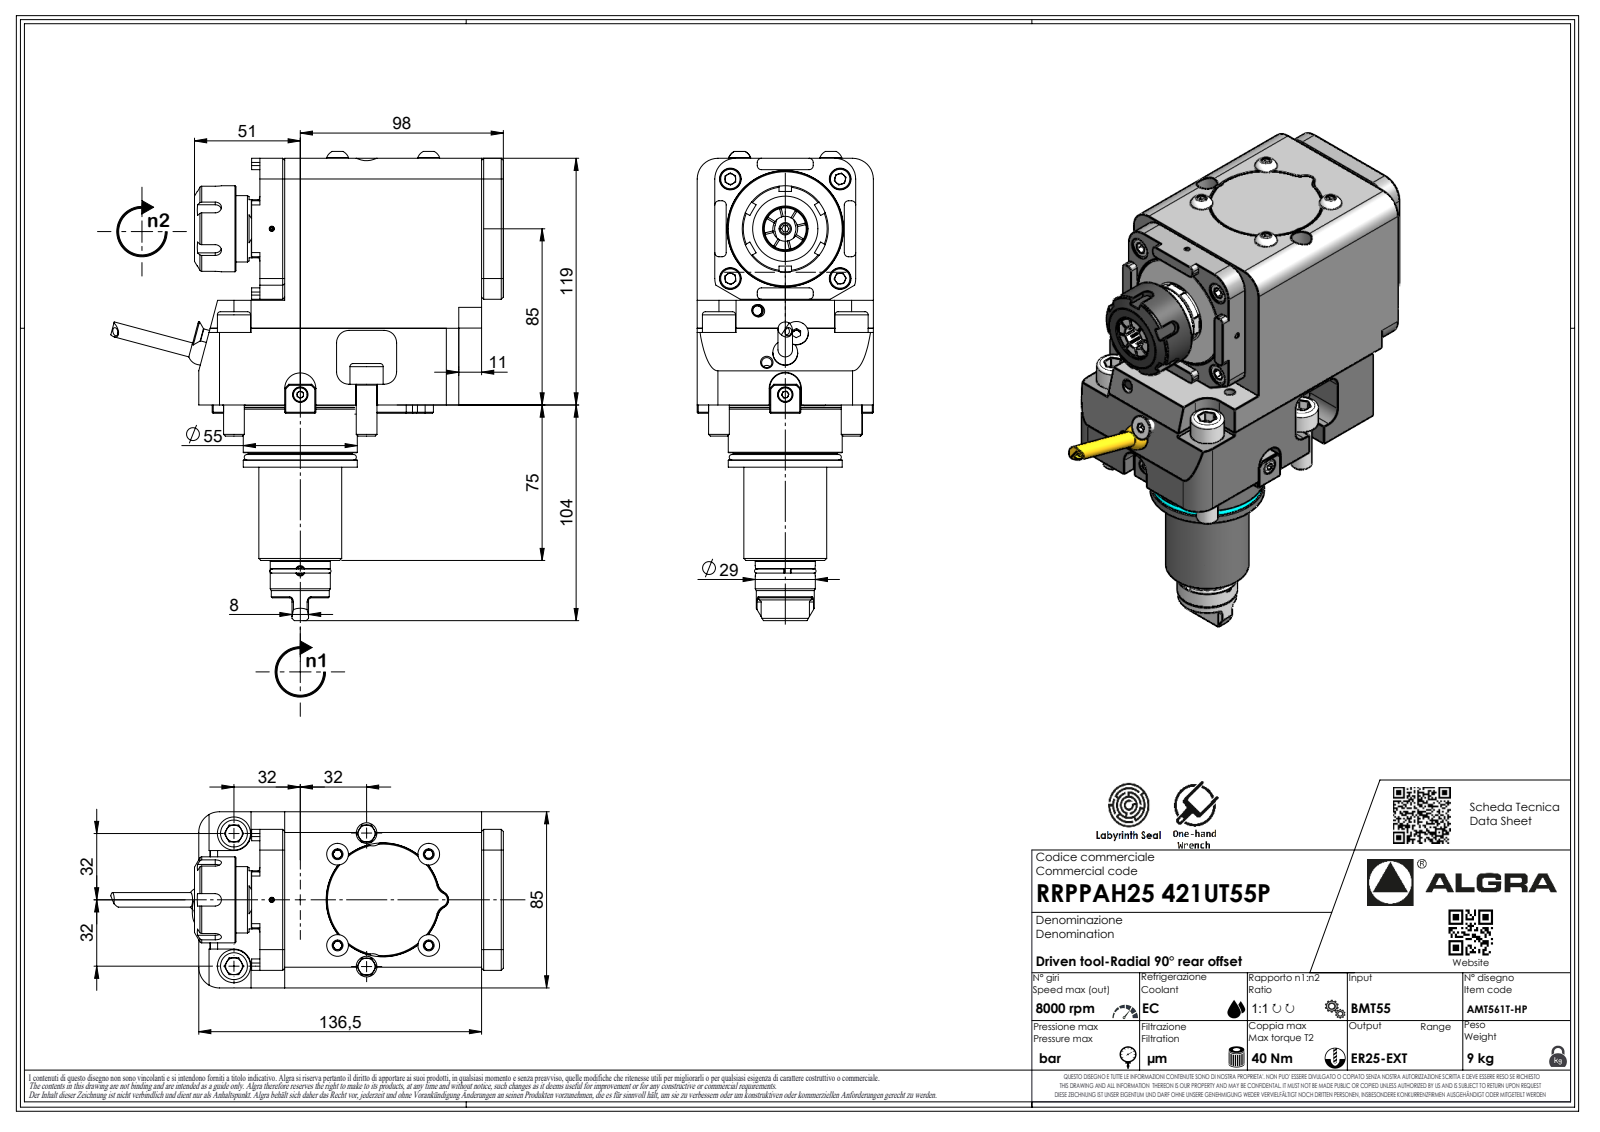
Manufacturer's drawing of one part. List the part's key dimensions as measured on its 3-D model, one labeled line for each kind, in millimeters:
Part name (STEP PRODUCT): RRPPAH25421UT55P
STEP written by: SolidWorks 2023 (AUTOMOTIVE_DESIGN)
Units: millimetres
Bodies: 6 solids, 925 faces (580 planar, 163 cylindrical, 182 other)
Overall size (bounding box): 226.3 × 189.45 × 85
Volume: 1 300 000 mm³ · Surface area: 127 205 mm²
Round holes (diameter × count): ⌀10.5 ×2, ⌀12 ×2, ⌀2.1 ×1, ⌀4 ×1, ⌀5 ×1, ⌀6 ×1, ⌀8.8 ×1, ⌀60 ×1
Round bosses / shafts (diameter × count): ⌀16 ×4, ⌀10.5 ×4, ⌀10 ×4, ⌀57 ×1, ⌀55 ×1, ⌀54.6 ×1, ⌀50.2 ×1, ⌀41.5 ×1
Partial cylindrical surfaces — rounded edges, fillets, slot ends (radius × count): R2 ×23, R10 ×10, R0.33 ×7, R0.52 ×7, R3.7 ×7, R4 ×4, R6 ×4, R3 ×3
Main face-to-face distances: 85, 119, 10.5, 107, 21.5, 117.5, 37, 96, 11, 50.5
Hole centre spacings: 61, 67.91
